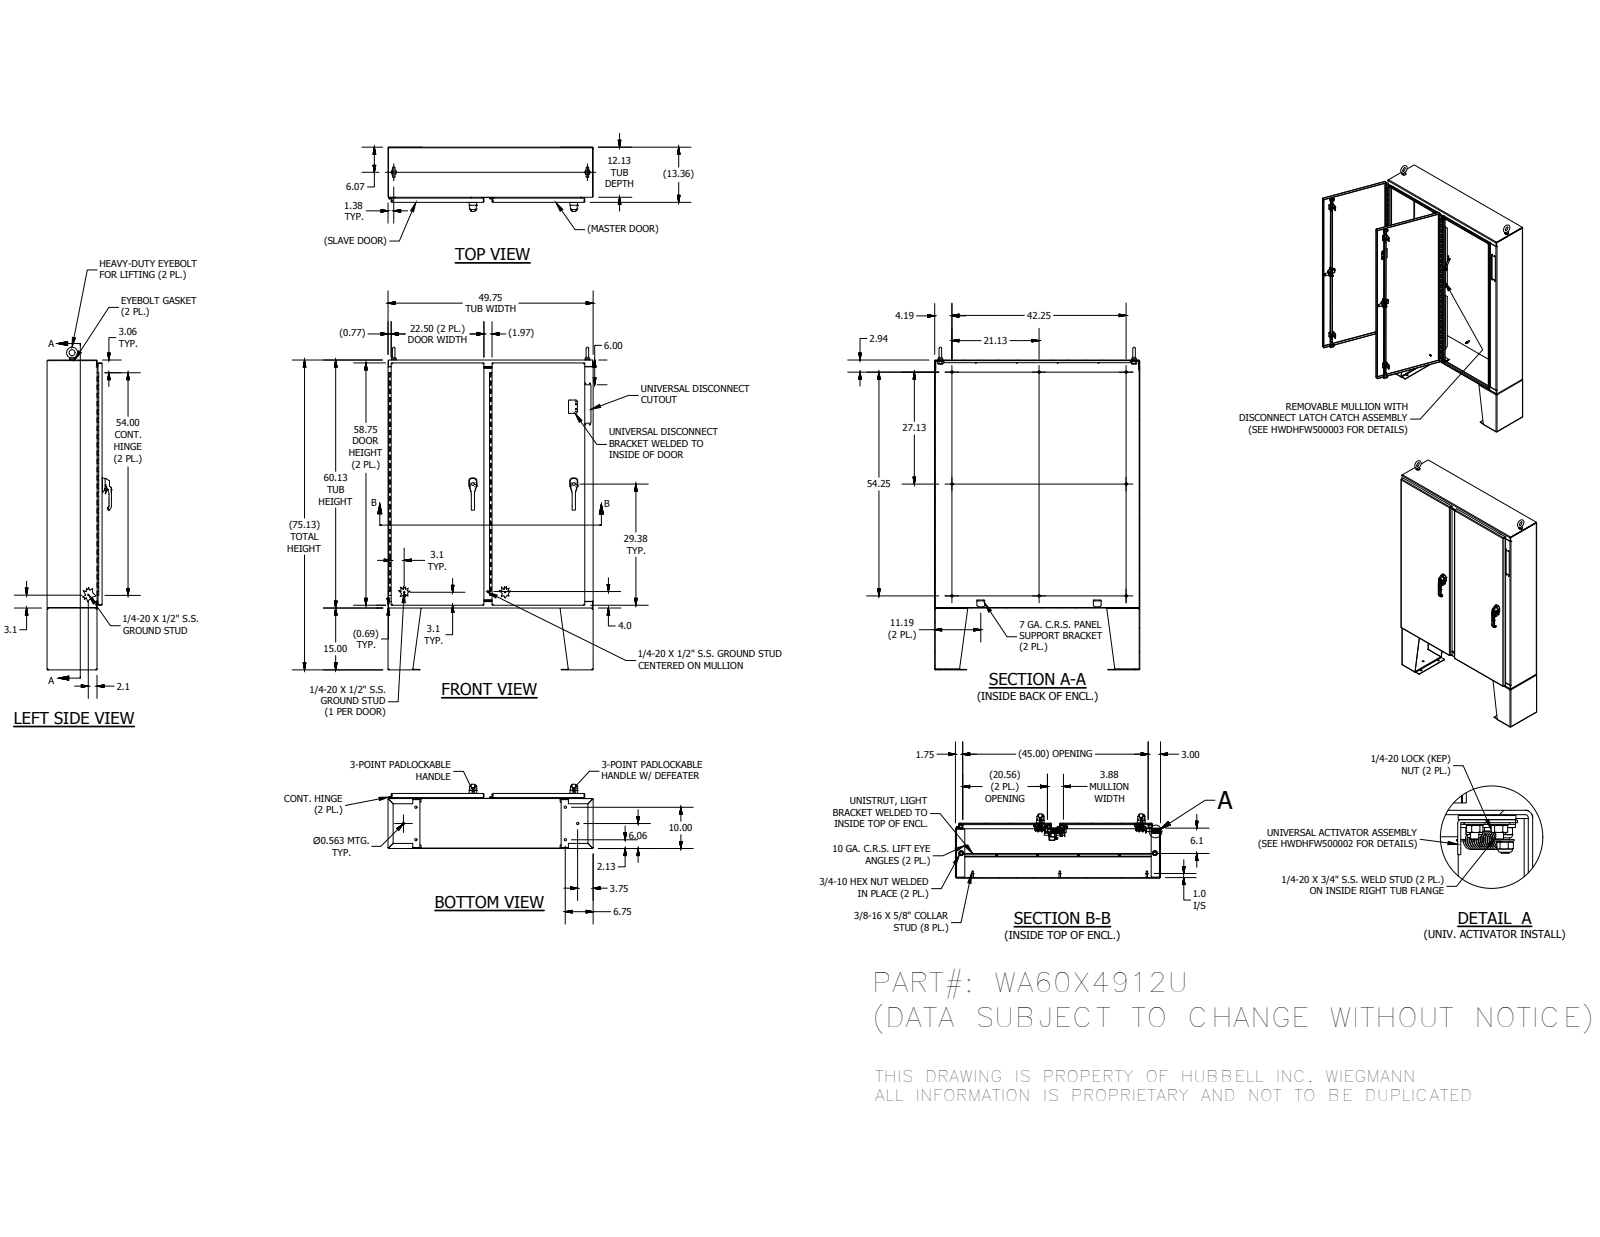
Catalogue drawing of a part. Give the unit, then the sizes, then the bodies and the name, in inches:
Units: inches
Overall size (bounding box): 78.248 × 49.75 × 15.608
Round holes (diameter × count): ⌀0.25 ×18, ⌀0.375 ×18, ⌀0.563 ×18, ⌀0.313 ×12, ⌀0.19 ×8, ⌀0.2 ×8, ⌀0.203 ×8, ⌀0.276 ×8, ⌀0.289 ×8, ⌀0.335 ×8, ⌀0.38 ×8, ⌀0.201 ×7
Round bosses / shafts (diameter × count): ⌀0.25 ×23, ⌀0.33 ×18, ⌀0.625 ×13, ⌀0.337 ×12, ⌀0.375 ×11, ⌀0.563 ×9, ⌀1 ×8, ⌀0.438 ×8
Partial cylindrical surfaces — rounded edges, fillets, slot ends (radius × count): R0.02 ×333, R0.012 ×203, R0.02 ×192, R0.019 ×42, R0.05 ×40, R0.125 ×37, R0.094 ×35, R0.063 ×27
Main face-to-face distances: 0.134, 13.217, 13.083, 13.35, 0.134, 49.616, 59.991, 11.991, 1.226, 11.857
Hole centre spacings: 0.024, 4.5, 2, 1.595, 1.601, 3.4, 24.469, 0.025
Volume: 1 530 in³ · Surface area: 23 930 in²
Bodies: 212 solids, 8687 faces (3990 planar, 2936 cylindrical, 1761 other)
Part name (STEP PRODUCT): WA60X4912UBLR; WAX4912UTOP; WAX4912UBTM; HFW332010S (+8 more)
STEP written by: Autodesk Inventor 2016 (AUTOMOTIVE_DESIGN)
